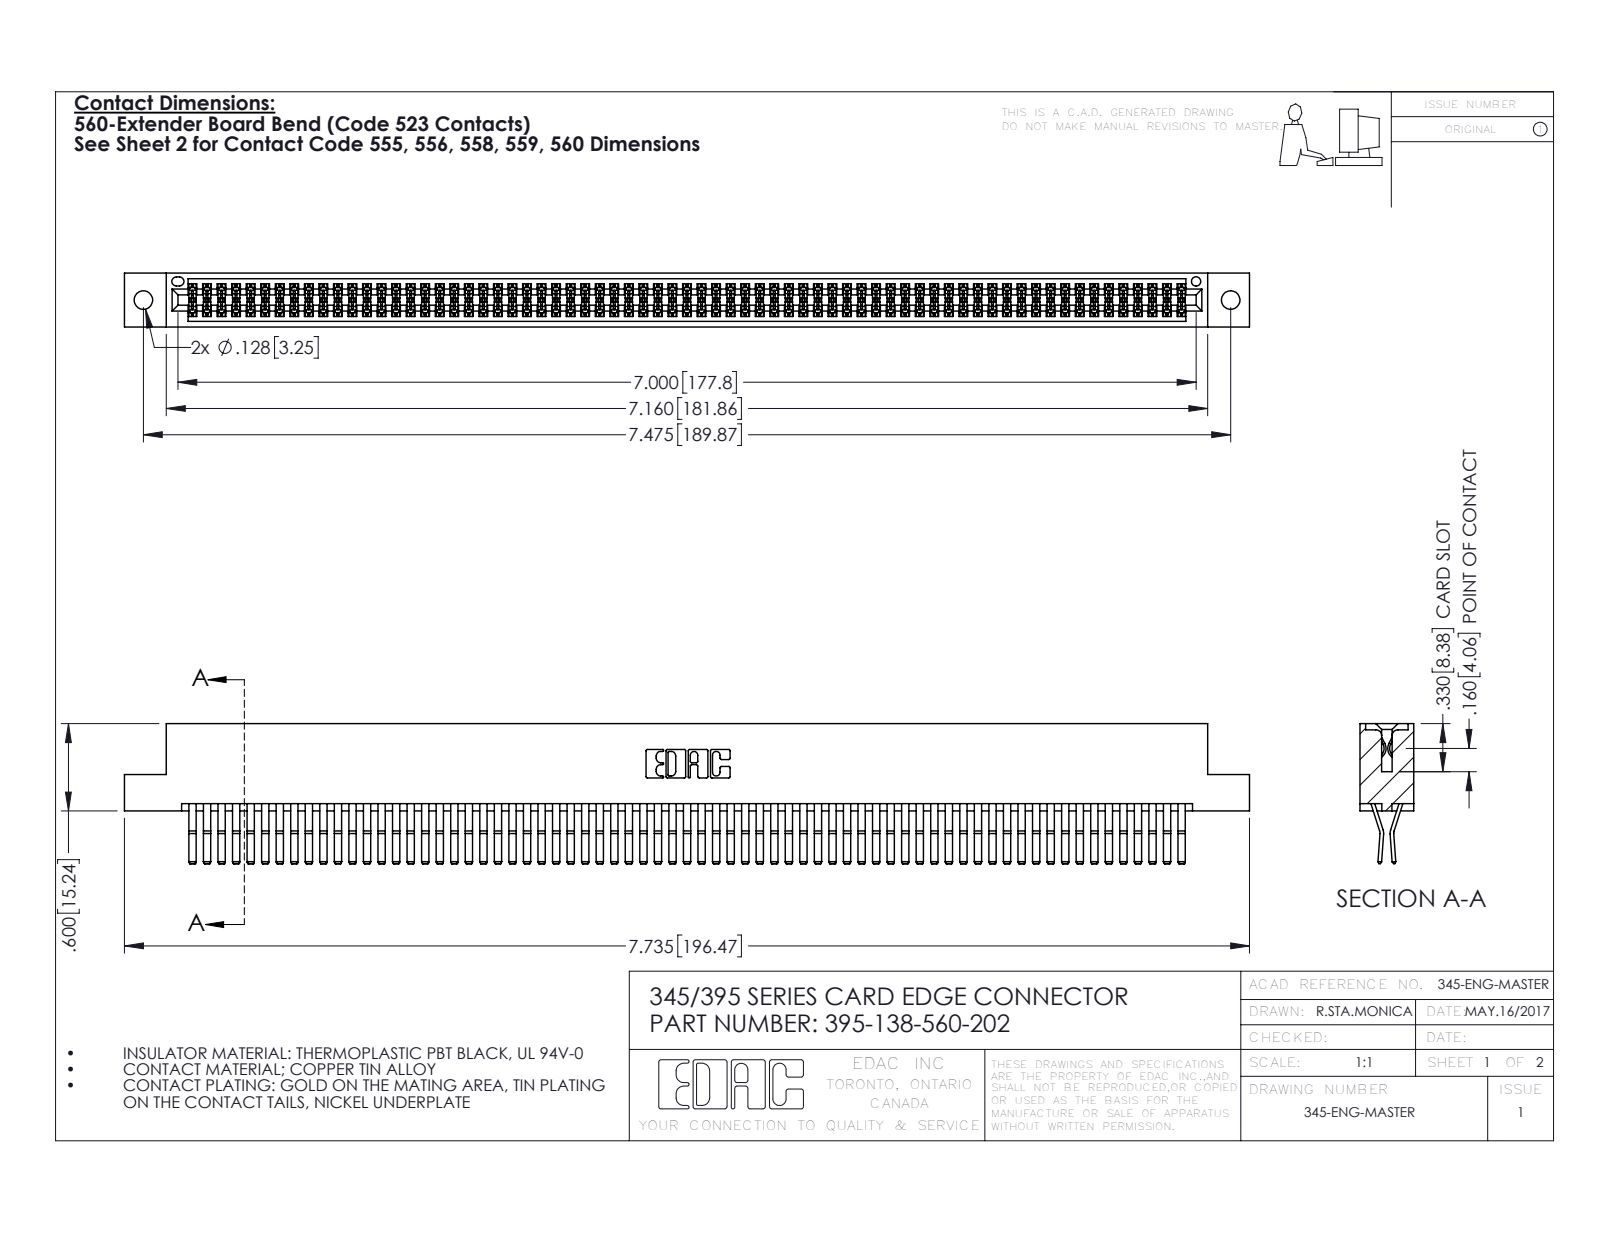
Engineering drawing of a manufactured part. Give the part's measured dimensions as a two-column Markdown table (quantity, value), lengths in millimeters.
| quantity | value |
| --- | --- |
| part name | 345-292-001_560 Tail; 395-138-560-202; 345 Part_Flush Mounting Lugs - 0.128 Dia |
| STEP written by | SolidWorks 2016 (CONFIG_CONTROL_DESIGN) |
| units | millimeters |
| bodies | 139 solids, 7302 faces (4634 planar, 2668 cylindrical, 0 other) |
| overall size | 196.5 × 24.4 × 9.4 |
| volume | 20 210 mm³ |
| surface area | 32 440 mm² |
| round holes (diameter × count) | 3.3 × 2, 1.6 × 1 |
| partial cylindrical surfaces (radius × count) | 0.2 × 207, 0.3 × 22, 0.2 × 6, 0.8 × 6, 0.7 × 3, 0.3 × 2, 0.4 × 2, 0.5 × 2 |
| main face-to-face distances | 0.6, 7.6, 1.8, 9.4, 5.1, 2.5, 6.9, 5.7, 4.4, 3.8 |
| hole center spacings | 6.9, 183.9, 189.9 |
